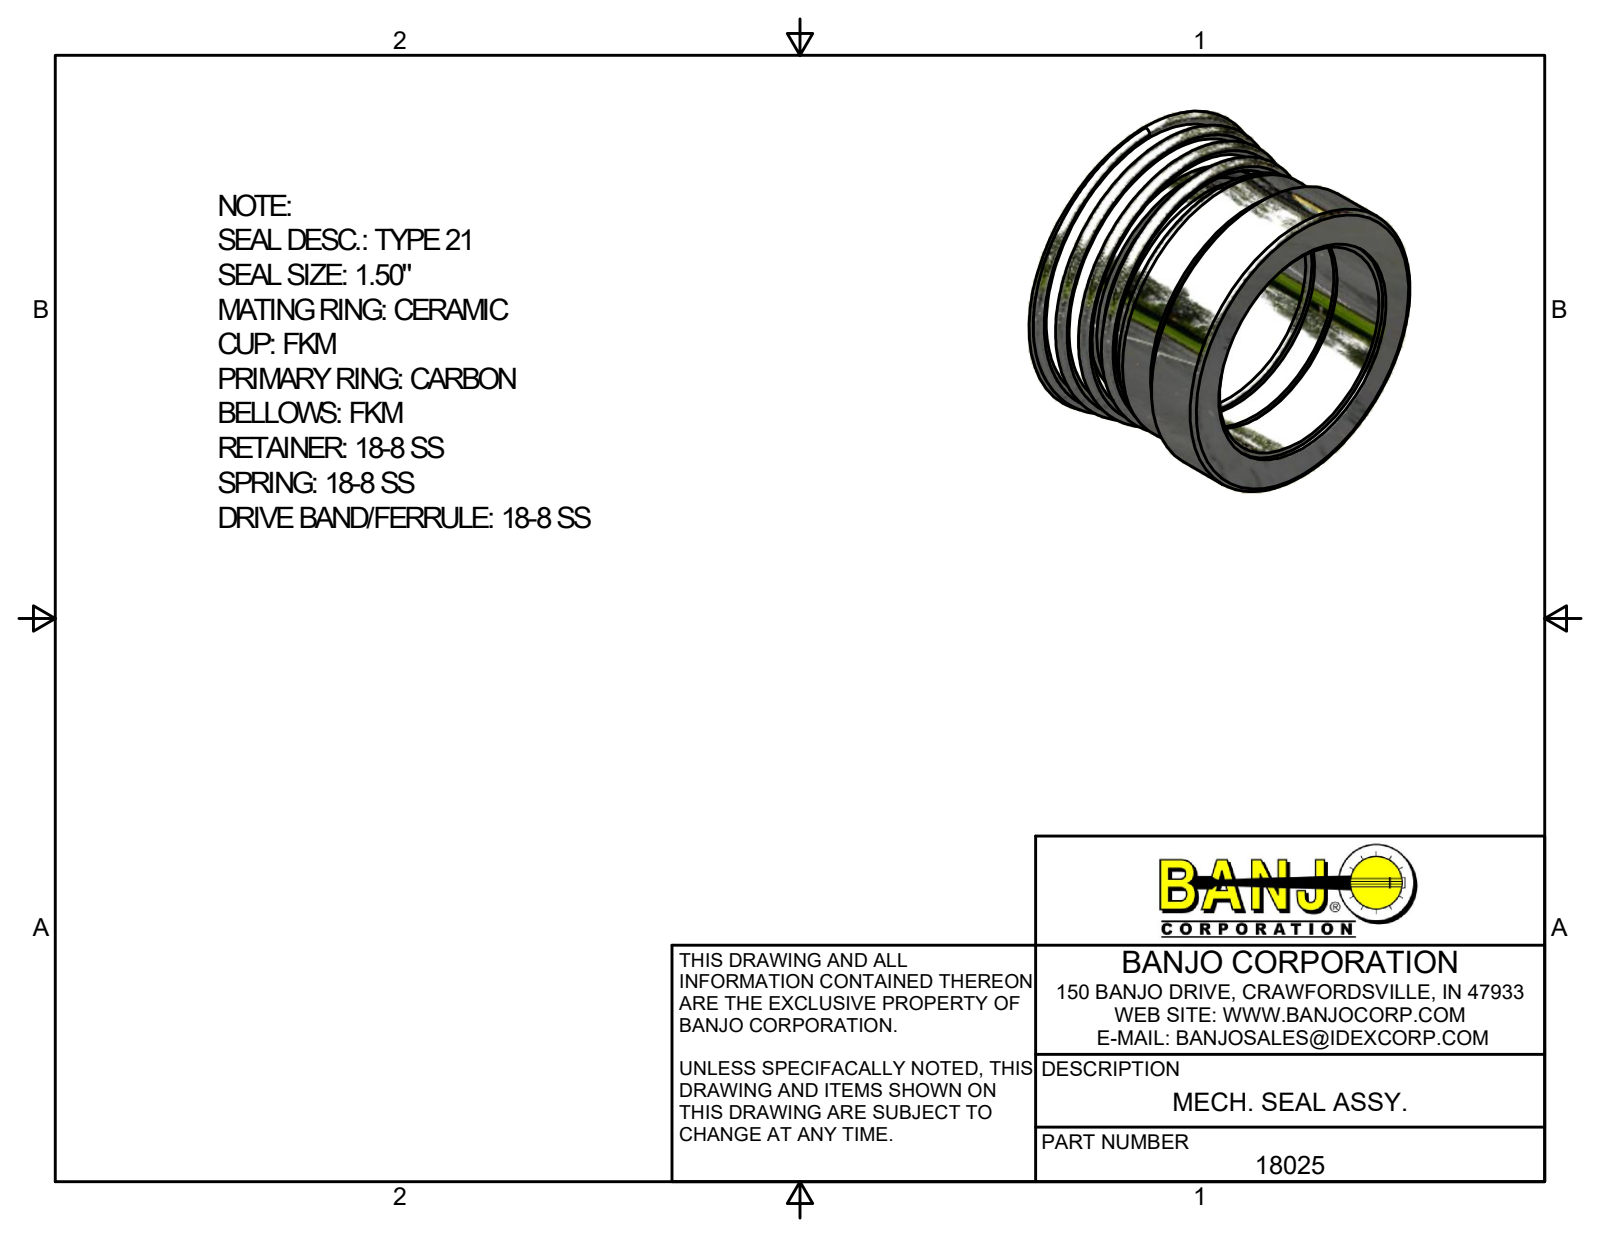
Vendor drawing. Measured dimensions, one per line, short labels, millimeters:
name: 18025
written by: Autodesk Inventor 2017 (AUTOMOTIVE_DESIGN)
unit: mm
bodies: 1 solid, 33 faces (14 planar, 11 cylindrical, 8 other)
size: 57.34 × 57.34 × 40.06
volume: 24 525 mm³; area: 17 566 mm²
holes: 1× ⌀38.1, 1× ⌀39.37, 1× ⌀40.96, 1× ⌀41.27
bosses: 1× ⌀53.97, 1× ⌀52.39, 1× ⌀47.31, 1× ⌀44.45, 1× ⌀41.15
face distances: 11.11, 6.35, 12.7, 19.05, 1.59, 27.76, 38.87, 4.76, 17.46, 0.79
